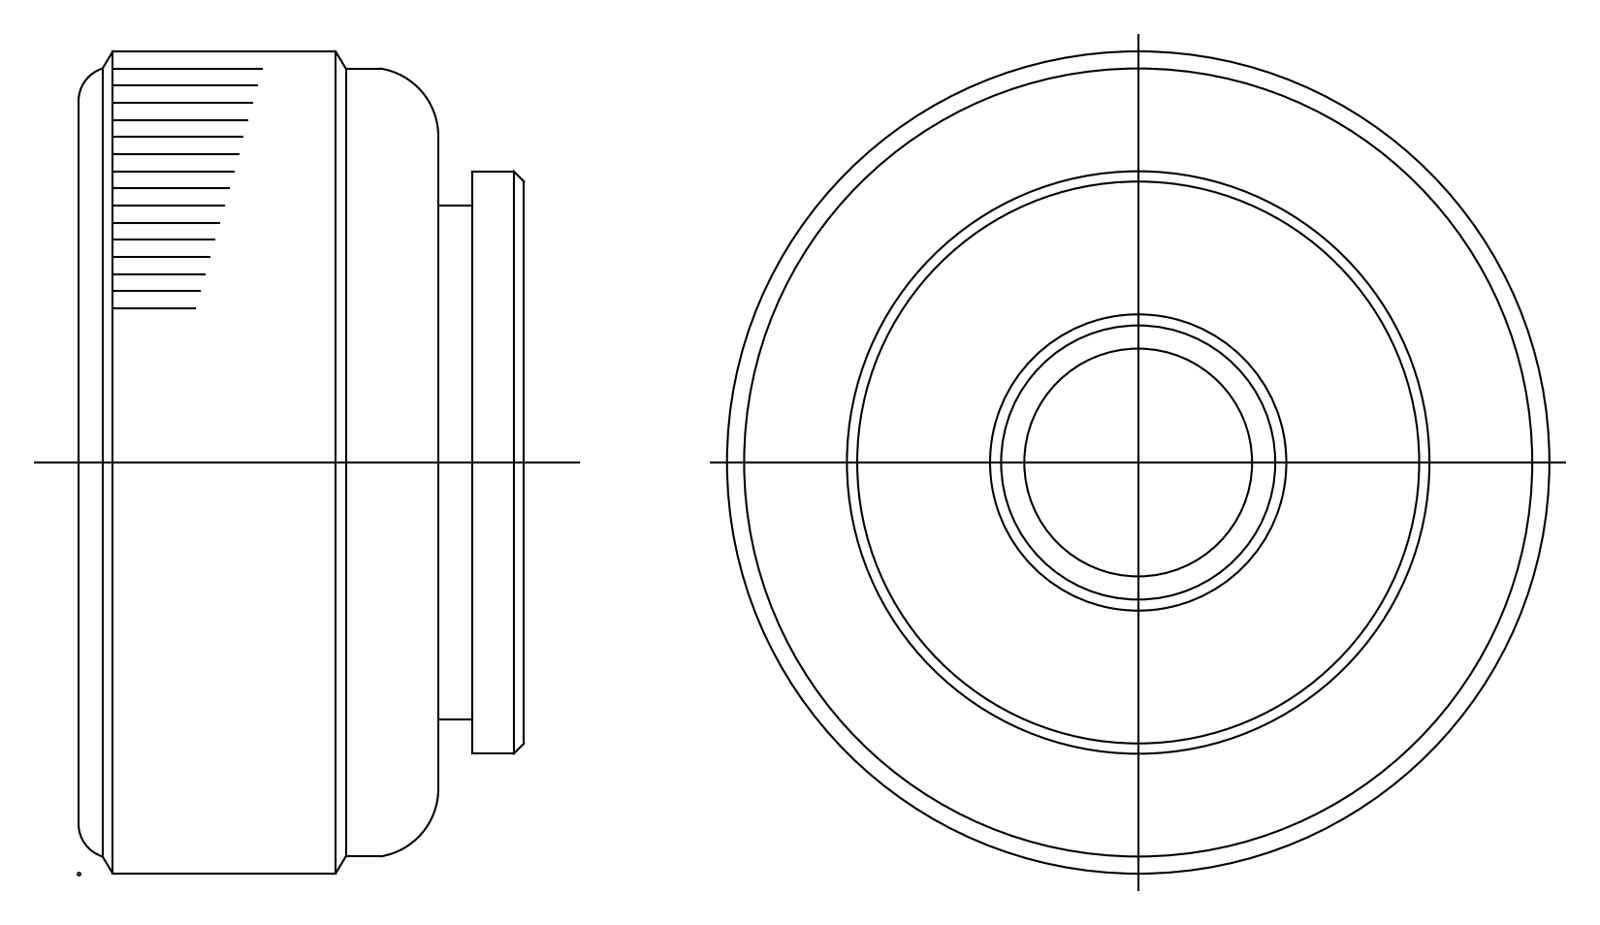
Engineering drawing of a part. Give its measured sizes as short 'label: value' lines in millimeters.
written by: spGate 20.6.3 (****-****-****-****) (AUTOMOTIVE_DESIGN)
unit: mm
bodies: 1 solid, 32 faces (4 planar, 12 cylindrical, 16 other)
size: 24 × 24 × 13
volume: 4 553 mm³; area: 2 018 mm²
holes: 1× ⌀6.65, 1× ⌀8
bosses: 1× ⌀24, 1× ⌀23, 1× ⌀17, 1× ⌀15
face distances: 13, 10.5, 2.5, 11.5, 1, 1.5
